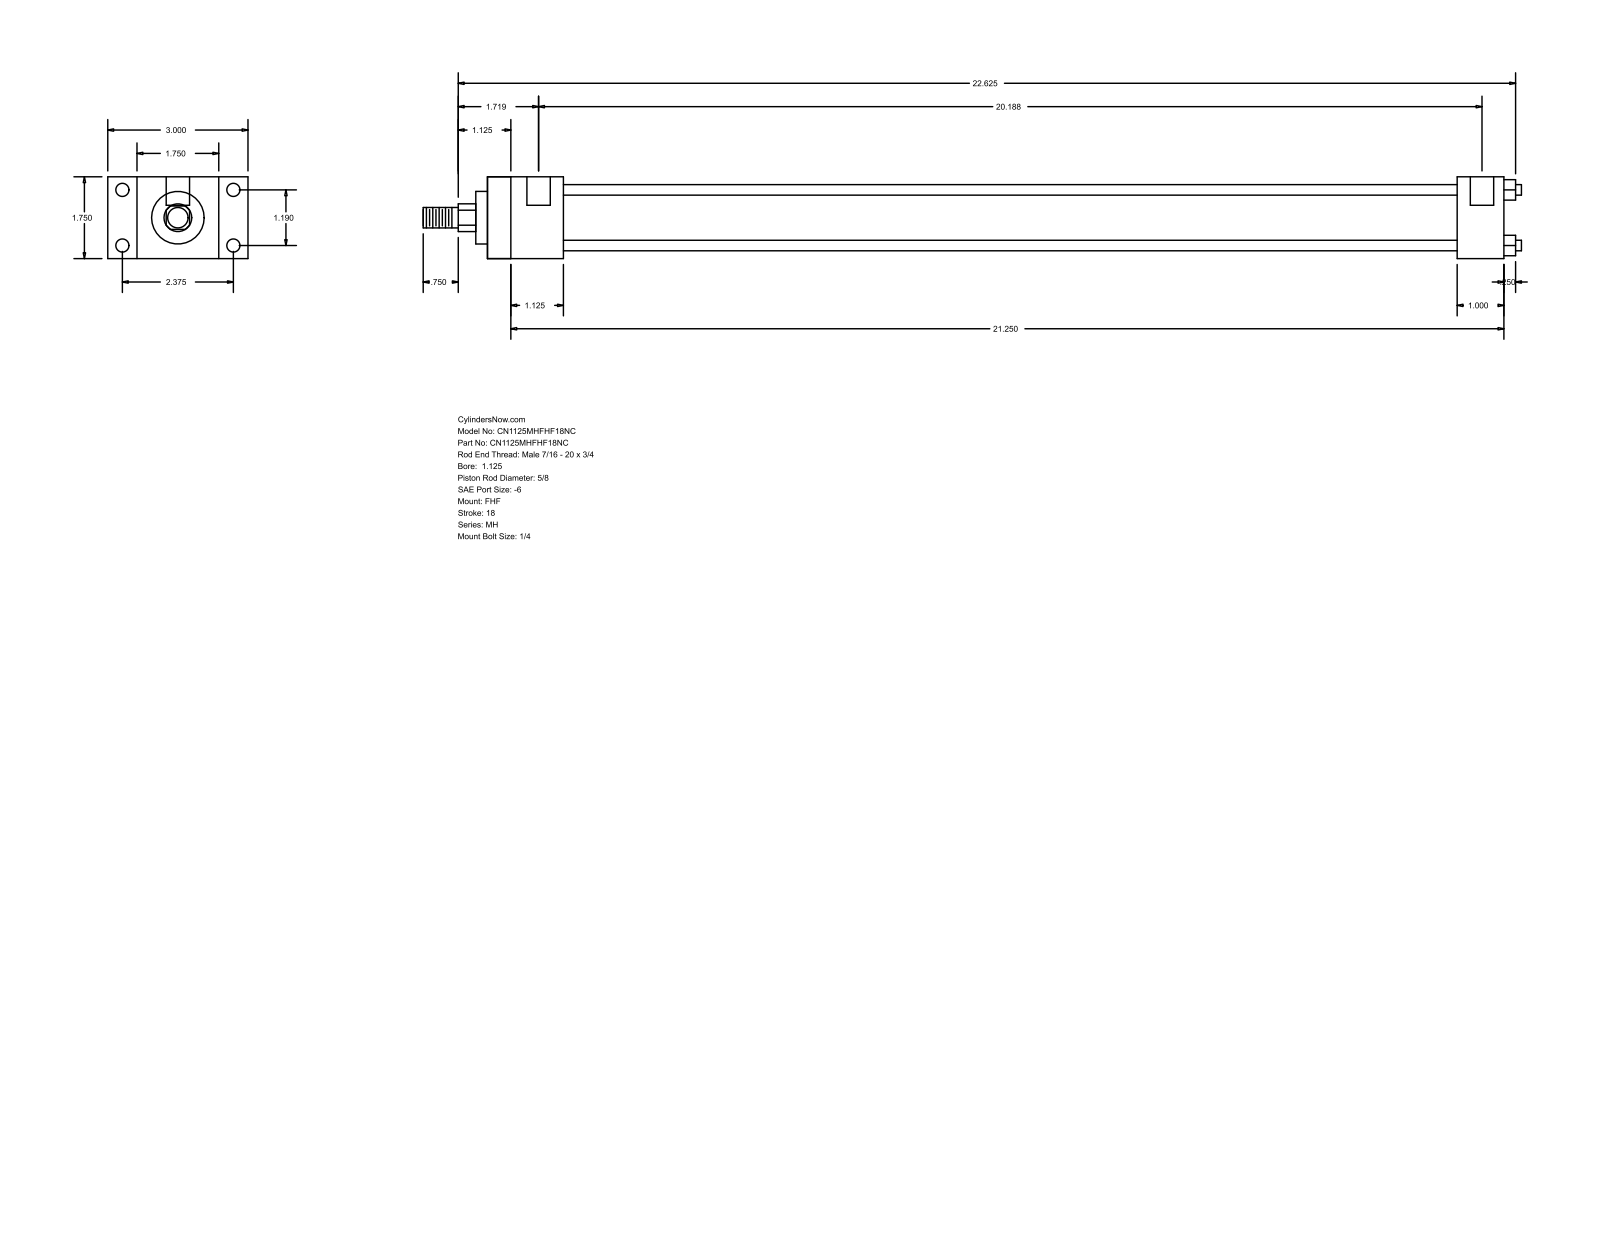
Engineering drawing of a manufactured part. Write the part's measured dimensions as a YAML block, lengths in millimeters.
part_name: "MH_FHF__0112_0.625"
step_written_by: "GSSL Pune (CONFIG_CONTROL_DESIGN)"
units: millimeters
bodies: {solids: 0, faces: 88, planar: 60, cylindrical: 28, other: 0}
overall_size: [596.9, 76.2, 44.45]
round_holes:
  - {diameter: 5.56, count: 4}
  - {diameter: 7.14, count: 4}
  - {diameter: 12.7, count: 2}
round_bosses_or_shafts:
  - {diameter: 5.71, count: 4}
  - {diameter: 34.92, count: 1}
  - {diameter: 28.57, count: 1}
  - {diameter: 15.88, count: 1}
  - {diameter: 11.11, count: 1}
partial_cylinders:
  - {radius: 7.54, count: 1}
face_to_face_distances: [44.46, 15.87, 60.33, 41.27, 76.2, 552.45, 511.18, 527.04, 485.77, 25.41]
hole_center_spacings: [30.22, 60.32, 67.47, 509.59, 3.17, 512.76]
